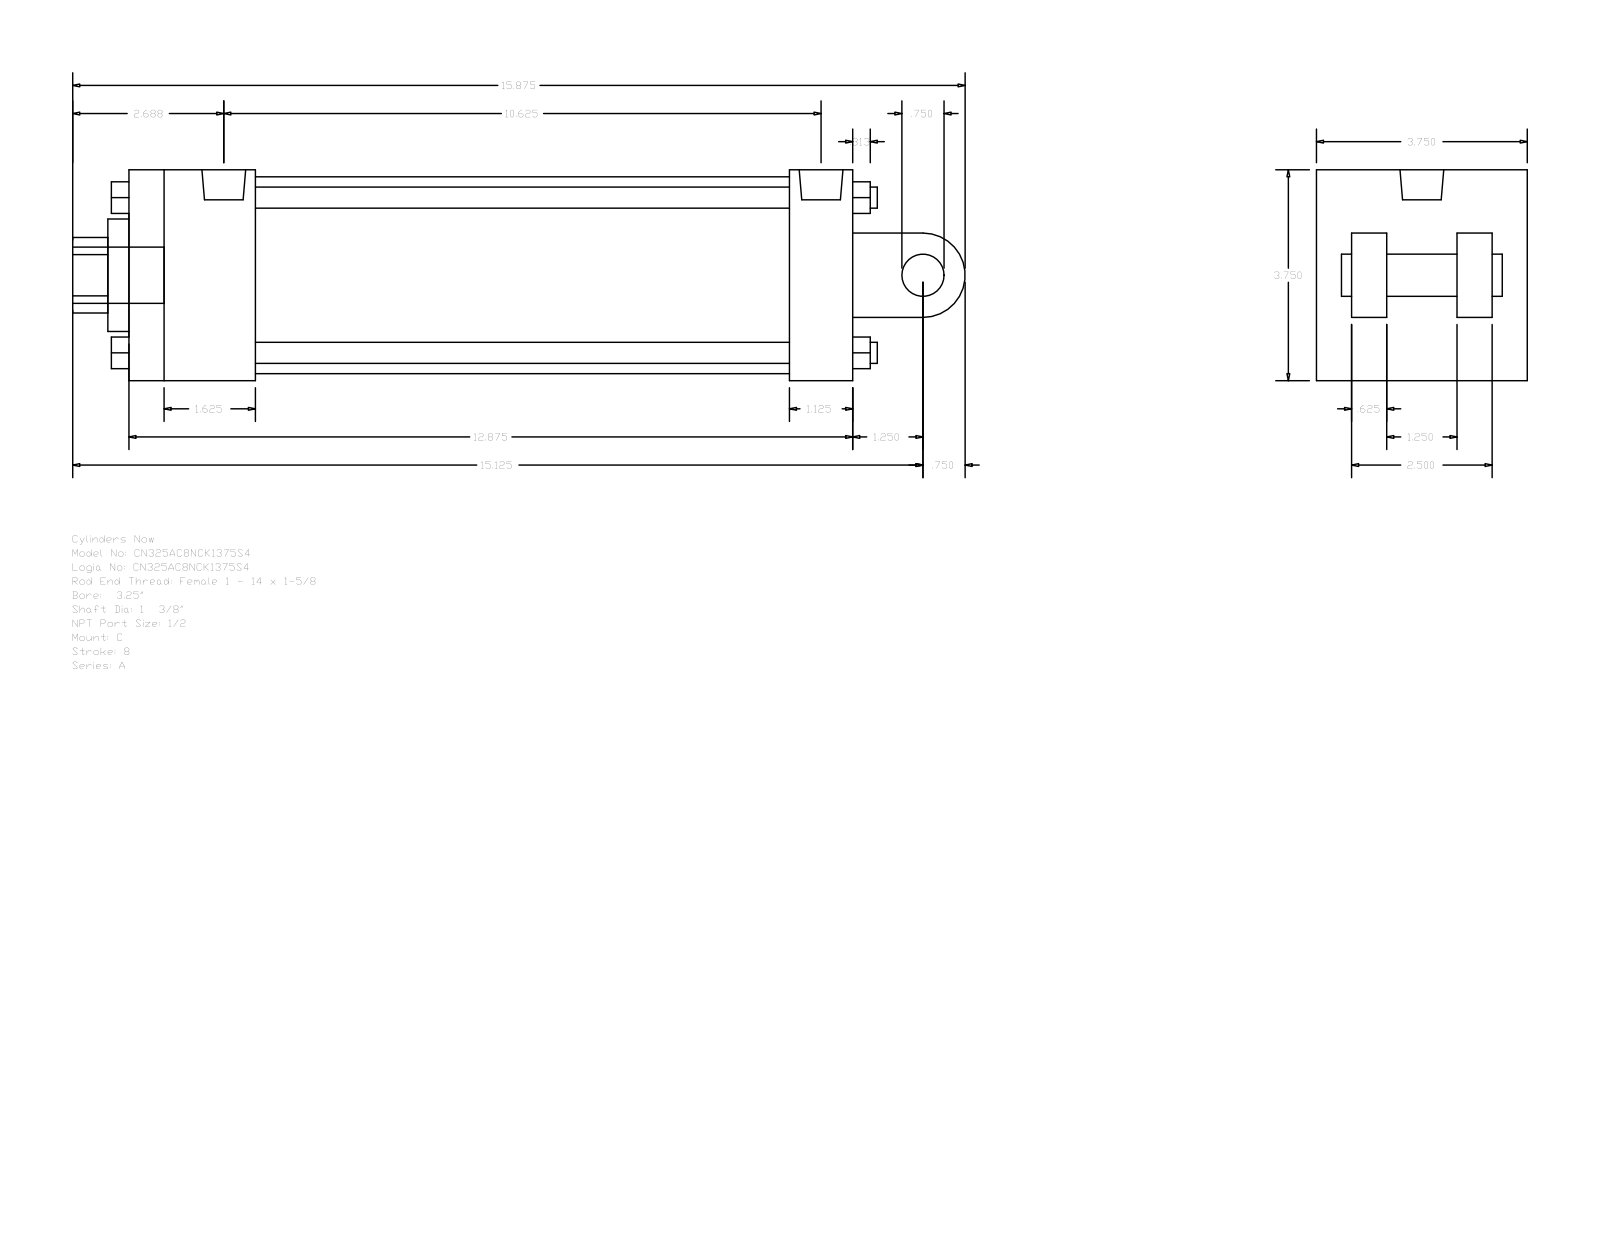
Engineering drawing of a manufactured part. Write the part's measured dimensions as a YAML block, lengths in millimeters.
part_name: "A_C__0325_1.375"
step_written_by: "GSSL Pune (CONFIG_CONTROL_DESIGN)"
units: millimeters
bodies: {solids: 0, faces: 135, planar: 102, cylindrical: 33, other: 0}
overall_size: [403.23, 95.25, 95.25]
round_holes:
  - {diameter: 8.73, count: 2}
  - {diameter: 19.77, count: 1}
  - {diameter: 34.92, count: 1}
  - {diameter: 50.8, count: 1}
  - {diameter: 88.9, count: 1}
round_bosses_or_shafts:
  - {diameter: 9.53, count: 4}
  - {diameter: 8.73, count: 2}
  - {diameter: 25.4, count: 1}
  - {diameter: 19.77, count: 1}
  - {diameter: 19.05, count: 1}
partial_cylinders:
  - {radius: 17.06, count: 1}
  - {radius: 19.05, count: 1}
face_to_face_distances: [95.24, 15.87, 327.03, 63.5, 66.67, 28.58, 79.37, 31.74, 47.63, 298.45]
hole_center_spacings: [3.18]
